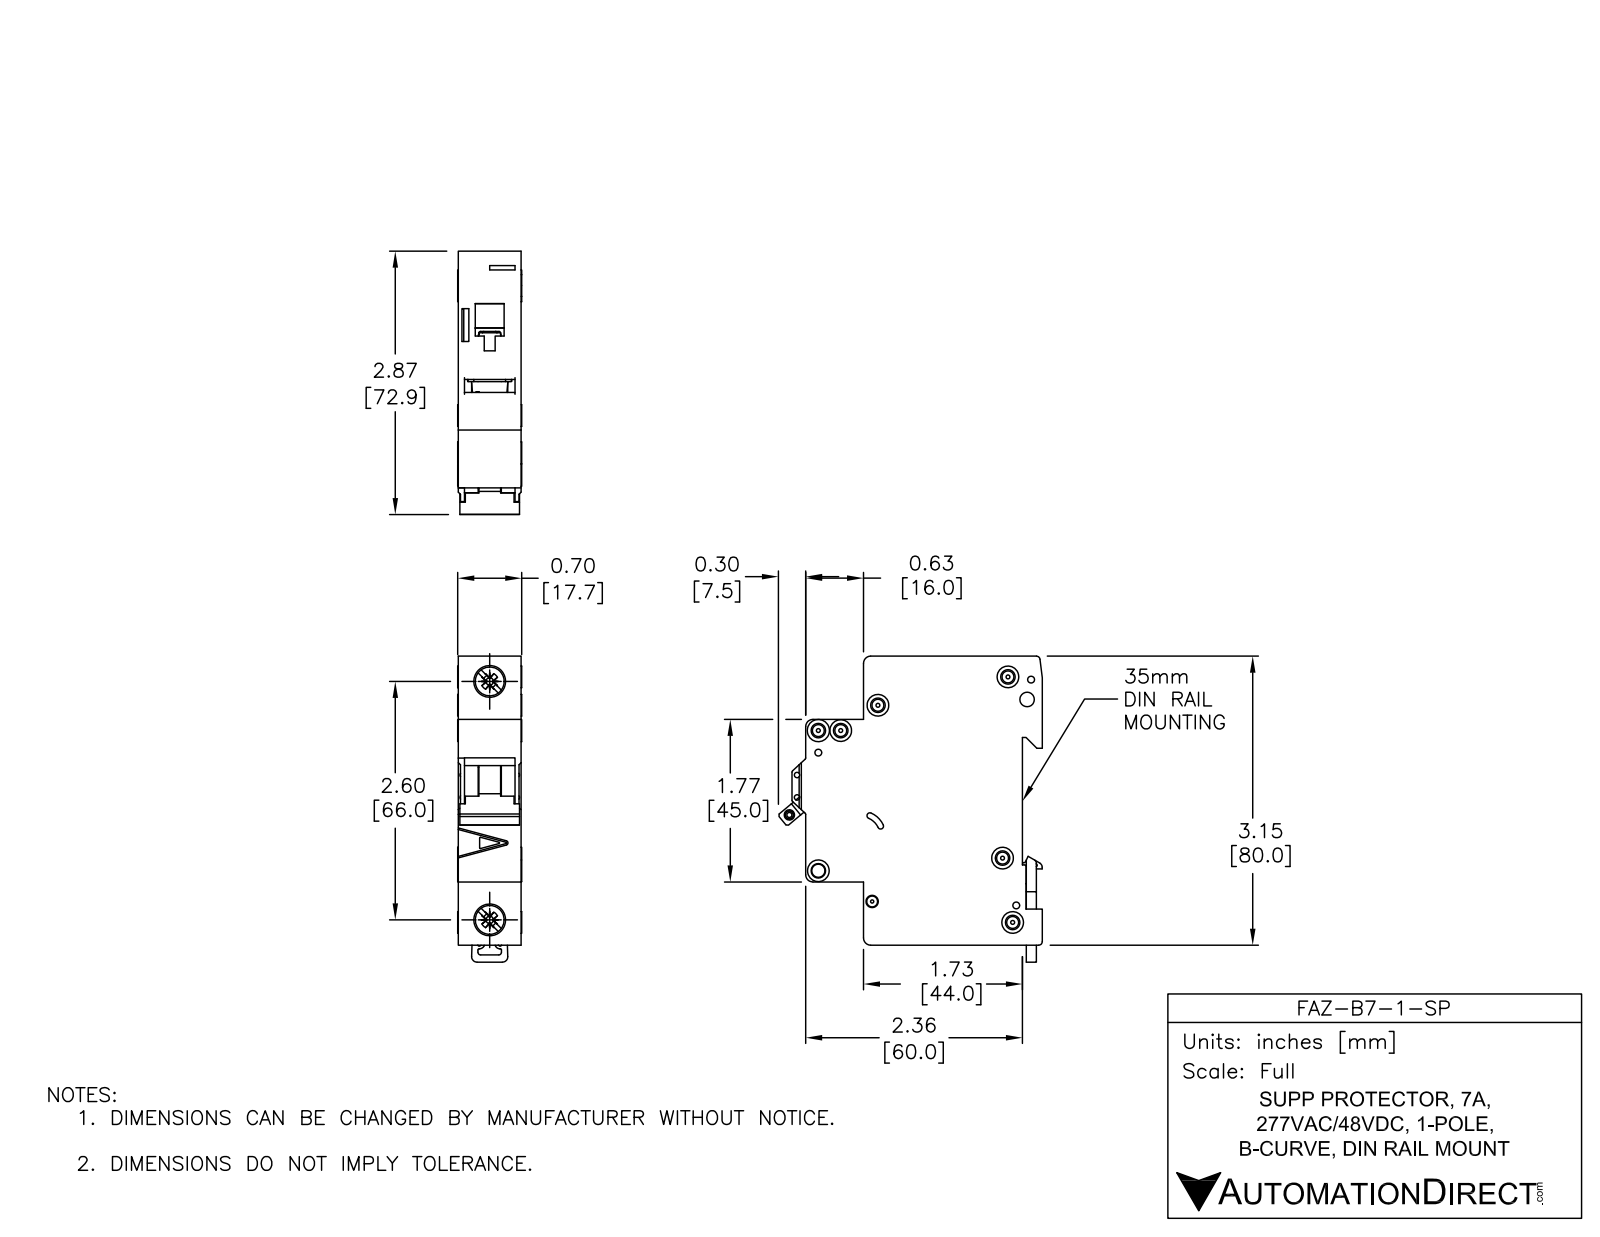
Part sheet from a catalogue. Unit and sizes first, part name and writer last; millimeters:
Units: millimetres
Overall size (bounding box): 84.78 × 73.04 × 17.7
Round holes (diameter × count): ⌀3.6 ×6, ⌀1.9 ×3, ⌀1.09 ×2, ⌀1.5 ×2, ⌀4 ×2, ⌀7.15 ×2, ⌀2.15 ×1, ⌀2.2 ×1, ⌀2.55 ×1, ⌀3.3 ×1, ⌀3.4 ×1
Round bosses / shafts (diameter × count): ⌀6 ×4, ⌀8.2 ×2, ⌀2.5 ×1
Partial cylindrical surfaces — rounded edges, fillets, slot ends (radius × count): R0.25 ×30, R0.5 ×13, R2 ×8, R0.2 ×5, R1 ×4, R0.8 ×2, R3 ×2, R1.5 ×1
Main face-to-face distances: 17.5, 79.48, 5.5, 49.5, 44, 65.5, 60, 16, 1.75, 15.75
Hole centre spacings: 6.2, 13.64, 4.81, 5.19, 5.61, 6.1, 6.44, 8.19
Volume: 74 935 mm³ · Surface area: 19 545 mm²
Bodies: 5 solids, 558 faces (235 planar, 202 cylindrical, 121 other)
Part name (STEP PRODUCT): FAZ-B7-1-SP
STEP written by: SolidWorks 2014 (AUTOMOTIVE_DESIGN)
